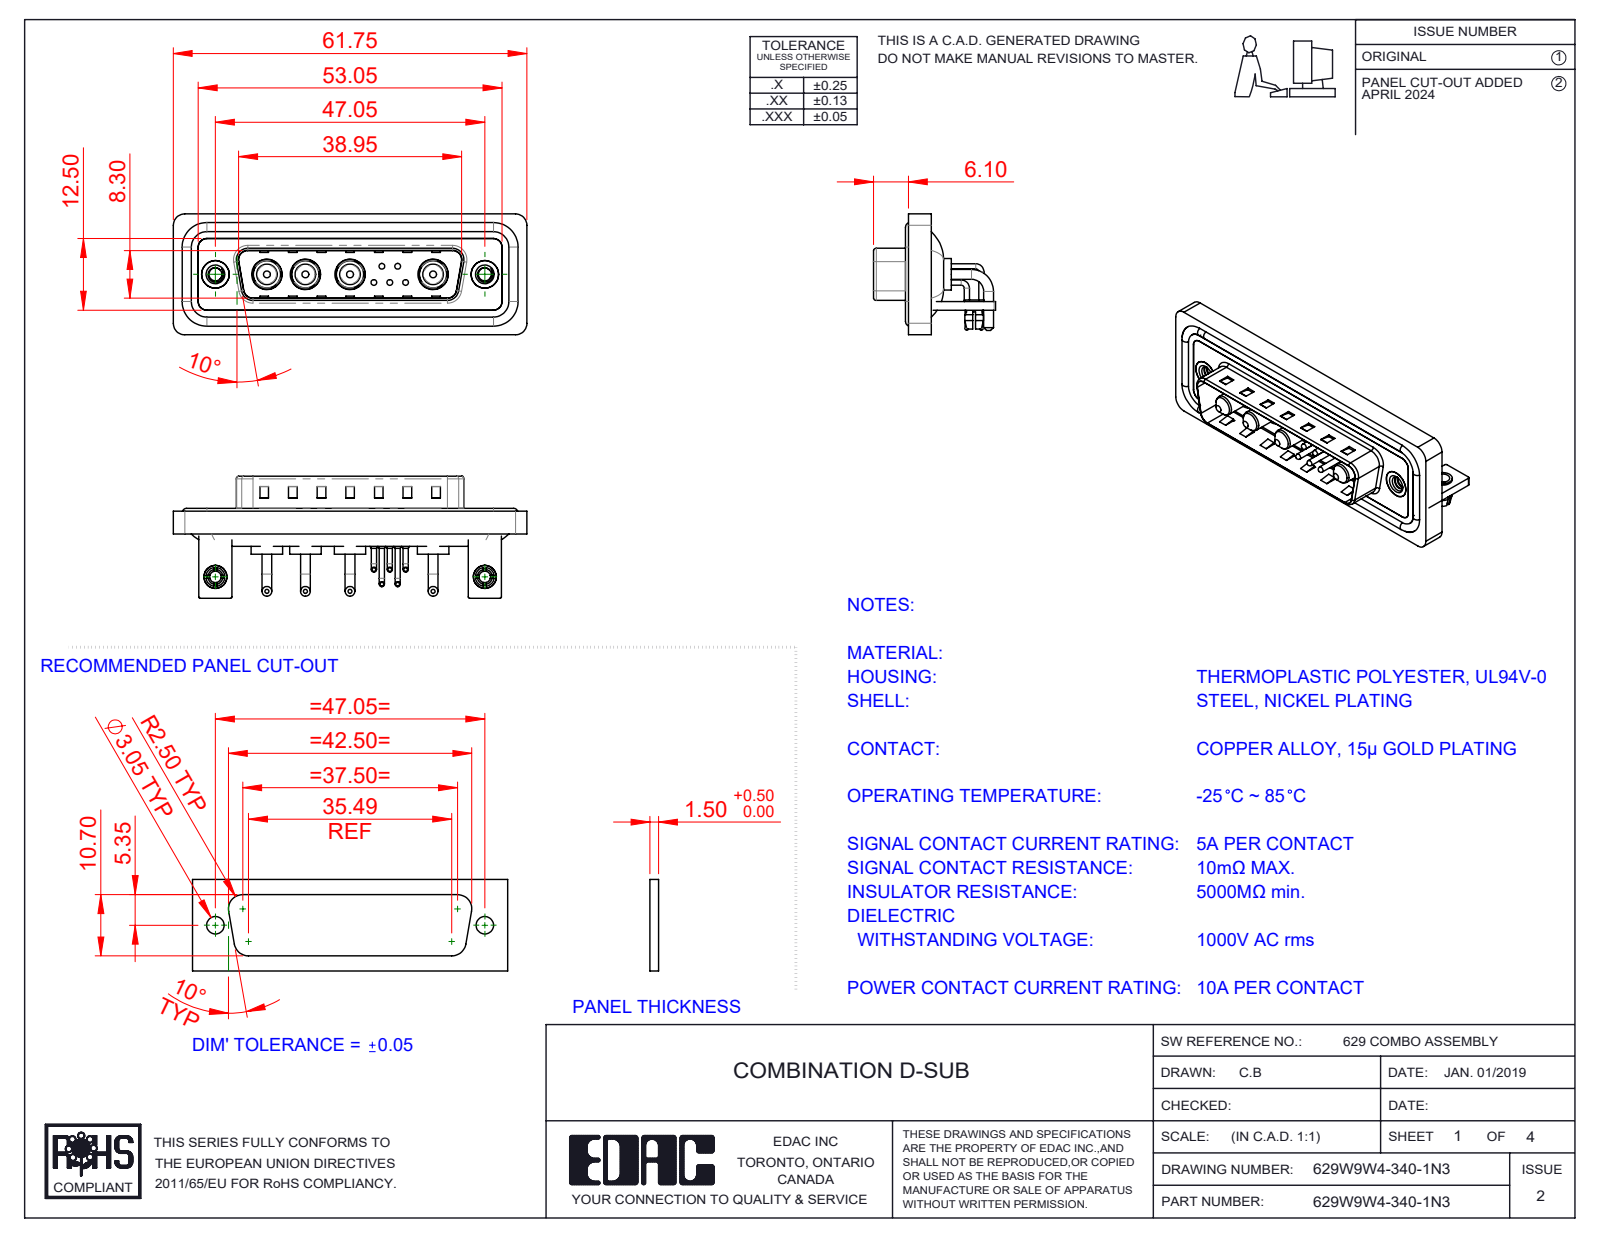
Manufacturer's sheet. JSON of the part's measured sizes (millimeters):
{"part_name": "629Combo Contact Row 2; 629Combo Stabilizer Bracket; 629Combo Board Lock; 629Combo Shell Front_25 Contacts (+7 more)", "step_written_by": "SolidWorks 2023 (CONFIG_CONTROL_DESIGN)", "units": "millimeters", "bodies": {"solids": 24, "faces": 1337, "planar": 637, "cylindrical": 502, "other": 198}, "overall_size": [61.75, 21.3, 21.1], "volume_mm3": 7786, "surface_area_mm2": 12970, "round_holes": [[2, 7], [0.75, 5], [1.6, 5], [4.85, 4], [5.3, 4], [2.26, 2], [2.5, 2], [3.2, 2], [4, 2], [4.8, 2], [5, 2]], "round_bosses_or_shafts": [[0.9, 10], [1.7, 8], [1.5, 5], [1, 5], [0.65, 5], [5.5, 4], [5.2, 4], [4.75, 4]], "partial_cylinders_radius": [[2, 19], [1.5, 18], [0.25, 16], [0.5, 9], [1.6, 8], [1.01, 5], [0.6, 4], [0.65, 4]], "face_to_face_distances": [0.4, 1.5, 0.8, 2.9, 2.1, 1.1, 3.7, 4.1, 4.5, 1.6], "hole_center_spacings": [3.16, 2.77, 5.04, 14.5, 47.05, 2.78, 4.4, 4.41]}
